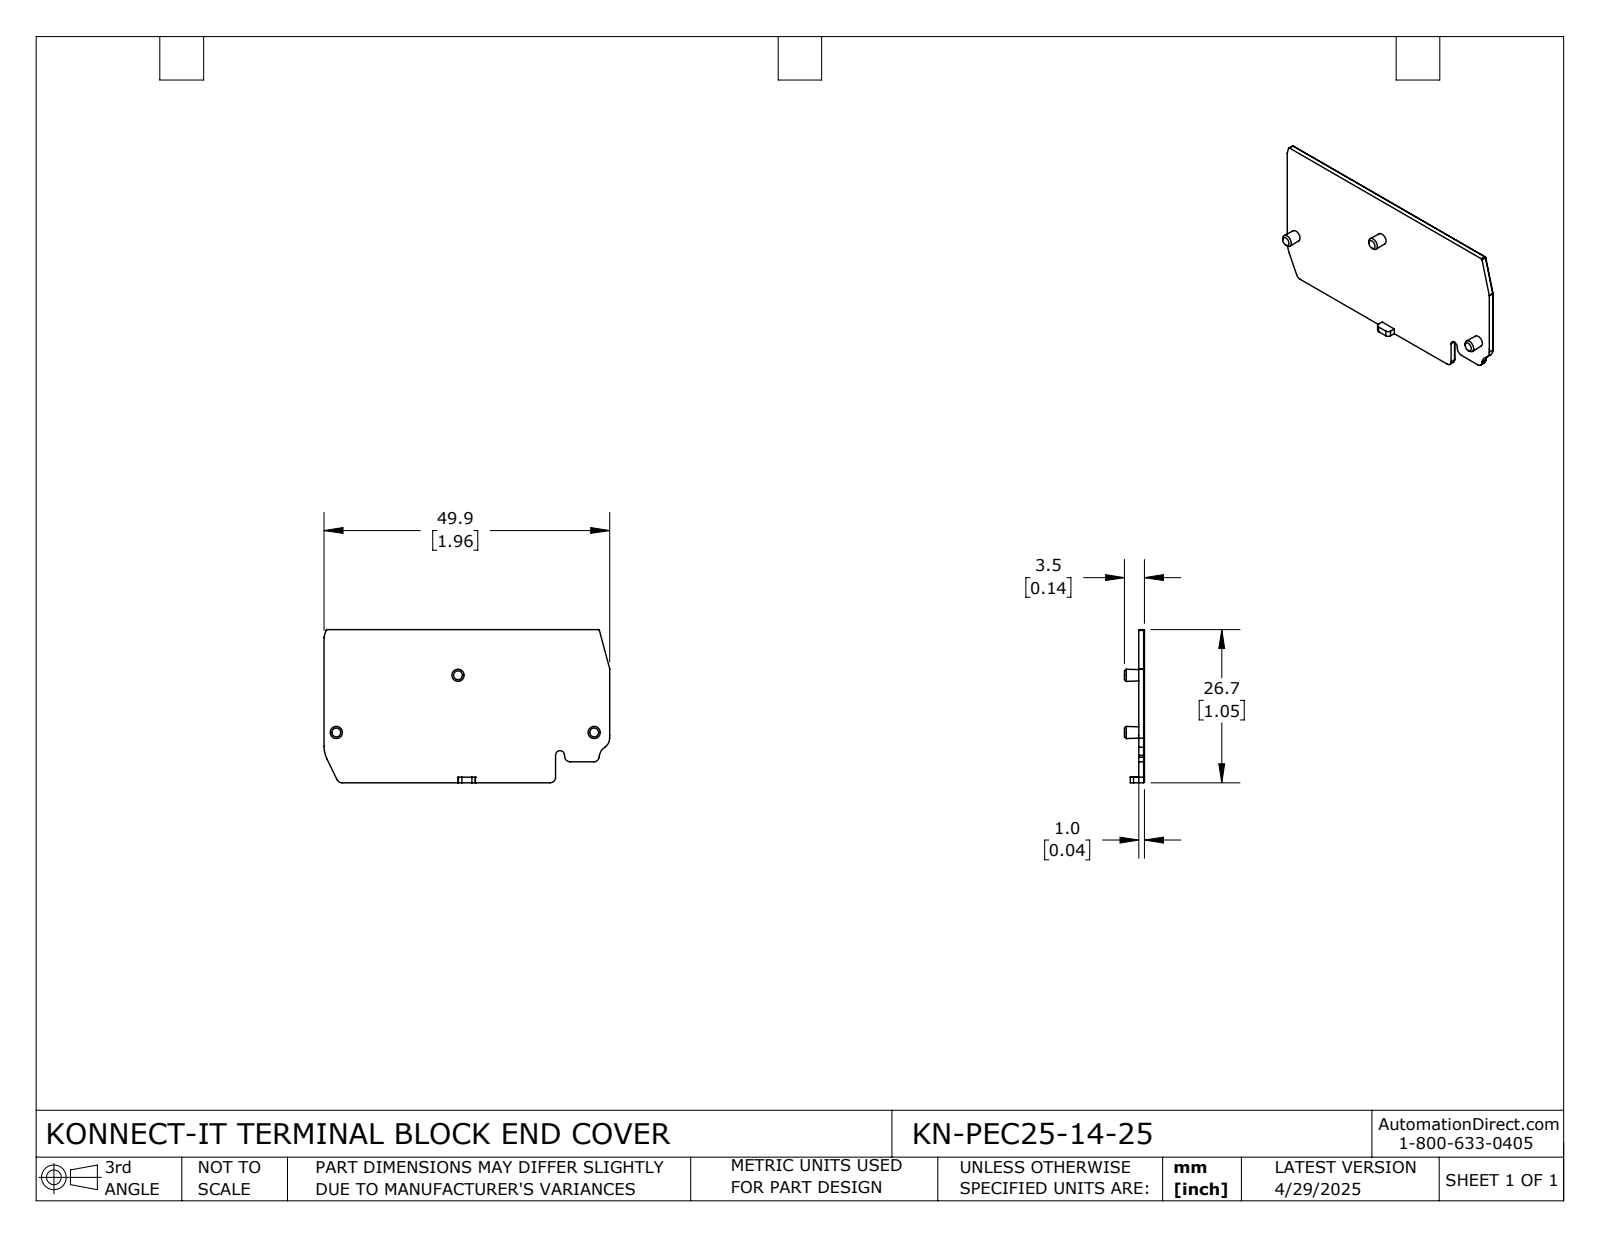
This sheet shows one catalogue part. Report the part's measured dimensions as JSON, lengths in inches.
{"part_name": "KN-PEC25-14-25", "step_written_by": "SolidWorks 2024 (CONFIG_CONTROL_DESIGN)", "units": "inches", "bodies": {"solids": 1, "faces": 71, "planar": 32, "cylindrical": 27, "other": 12}, "overall_size": [1.964, 1.053, 0.138], "volume_in3": 0.08, "surface_area_in2": 4.283, "partial_cylinders_radius": [[0.008, 4], [0.035, 4], [0.039, 4], [0.012, 3], [0.024, 2], [0.004, 1], [0.031, 1], [0.034, 1]], "face_to_face_distances": [0.039, 1.053, 0.033, 1.049, 1.963, 0.098, 0.132, 0.138, 1.045, 1.959]}
